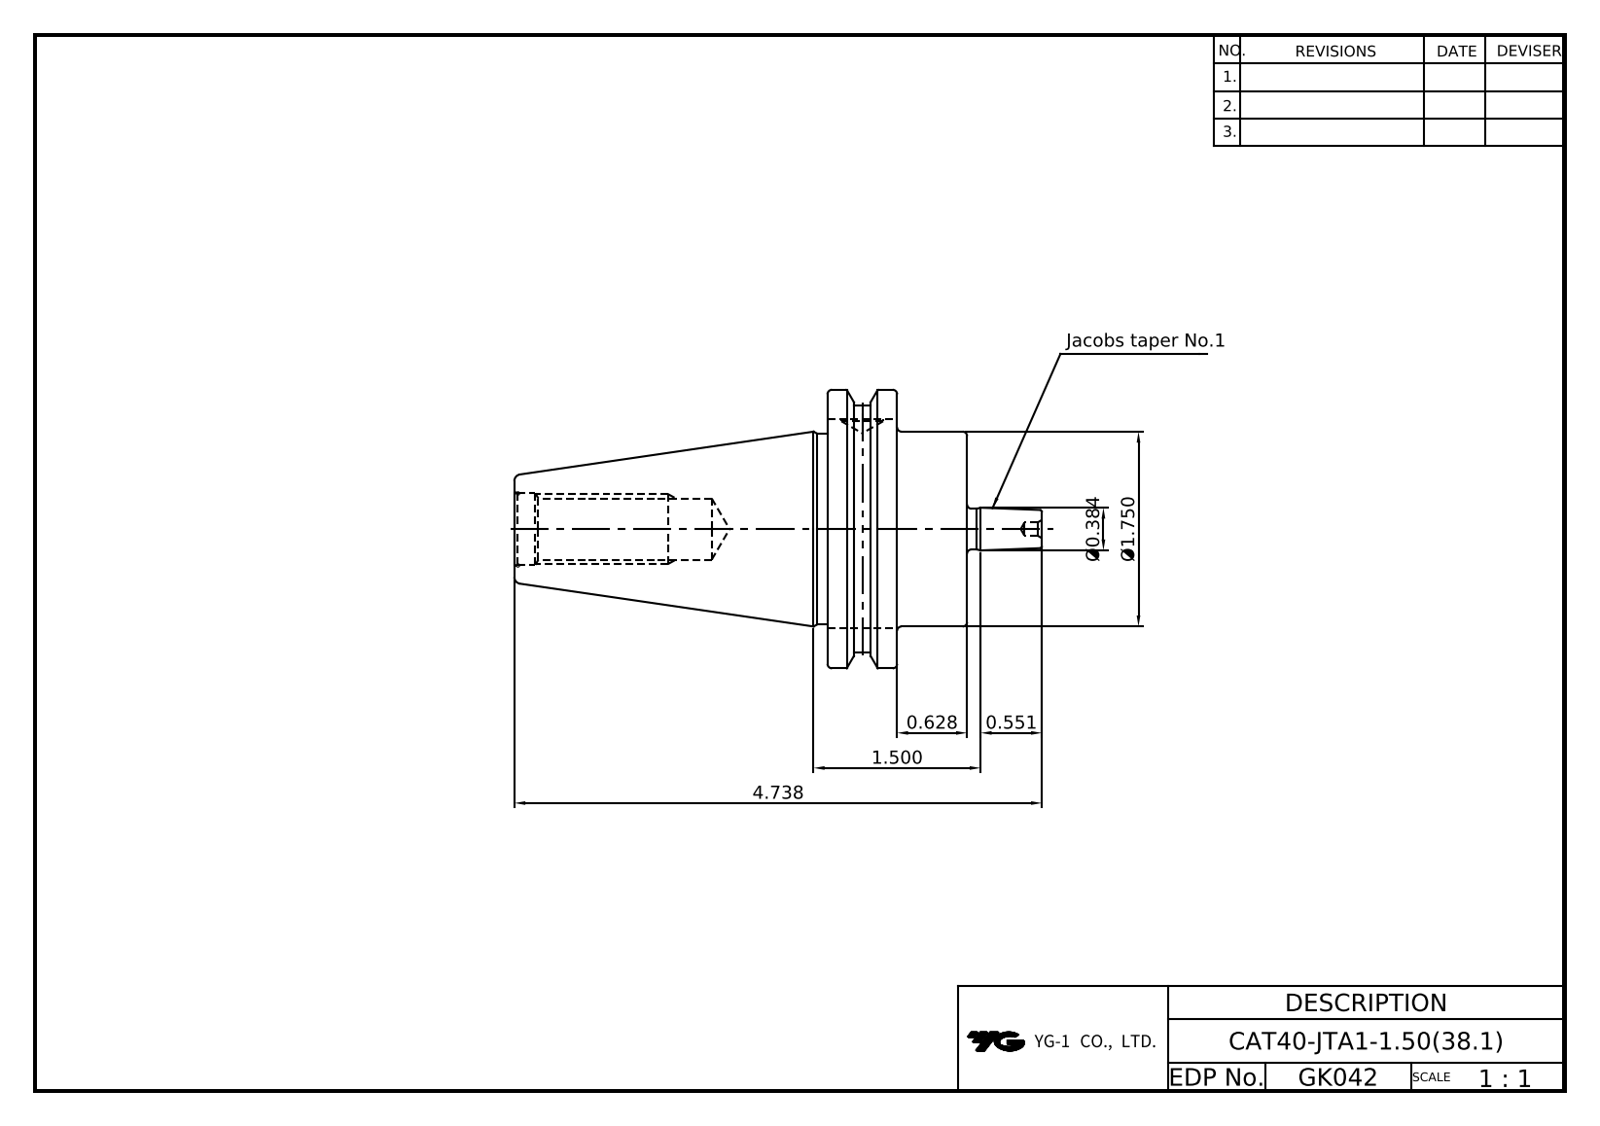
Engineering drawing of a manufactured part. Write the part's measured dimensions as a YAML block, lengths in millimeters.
part_name: "CAT40-JTA1-1.50(20231109)"
step_written_by: "Autodesk Inventor 2024 (AUTOMOTIVE_DESIGN)"
units: millimeters
bodies: {solids: 1, faces: 61, planar: 28, cylindrical: 12, other: 21}
overall_size: [120.35, 63.5, 61.09]
volume: 132658
surface_area: 21185
round_holes:
  - {diameter: 9.53, count: 1}
  - {diameter: 13.39, count: 1}
  - {diameter: 16.3, count: 1}
round_bosses_or_shafts:
  - {diameter: 63.5, count: 1}
  - {diameter: 56.3, count: 1}
  - {diameter: 44.45, count: 1}
  - {diameter: 43.6, count: 1}
  - {diameter: 9.3, count: 1}
face_to_face_distances: [31.83, 15.88, 15.95, 47.6, 16.38, 71.42, 87.3, 103.25, 77.46, 81.29]
